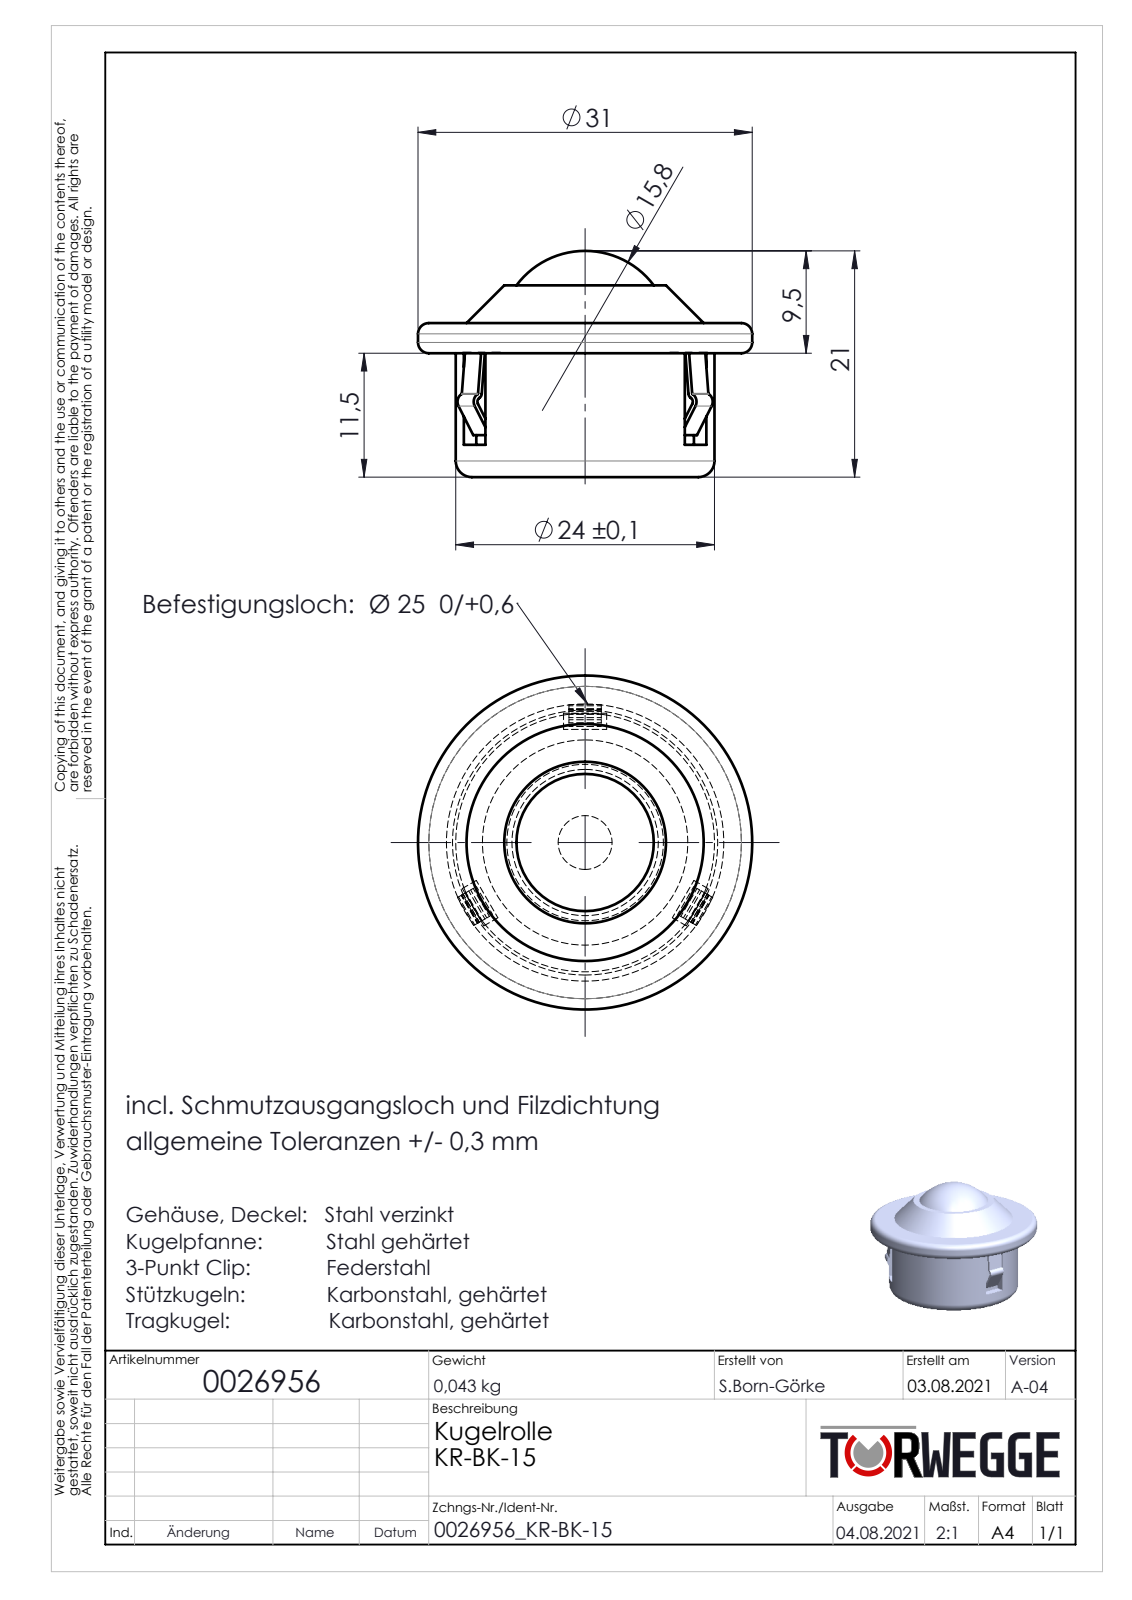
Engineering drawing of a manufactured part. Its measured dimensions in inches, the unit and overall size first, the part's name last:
Units: inches
Overall size (bounding box): 1.22 × 1.22 × 0.827
Round holes (diameter × count): ⌀0.197 ×1, ⌀1.013 ×1
Round bosses / shafts (diameter × count): ⌀1.22 ×1, ⌀0.945 ×1
Partial cylindrical surfaces — rounded edges, fillets, slot ends (radius × count): R0.02 ×6, R0.004 ×3, R0.016 ×3, R0.031 ×3, R0.035 ×3
Main face-to-face distances: 0.11, 0.02, 0.138, 0.016, 0.091, 0.248, 0.228, 0.157, 0.394, 0.413
Volume: 0.478 in³ · Surface area: 4.738 in²
Bodies: 1 solid, 93 faces (50 planar, 26 cylindrical, 17 other)
Part name (STEP PRODUCT): 0026956
STEP written by: SolidWorks 2020 (AUTOMOTIVE_DESIGN)
